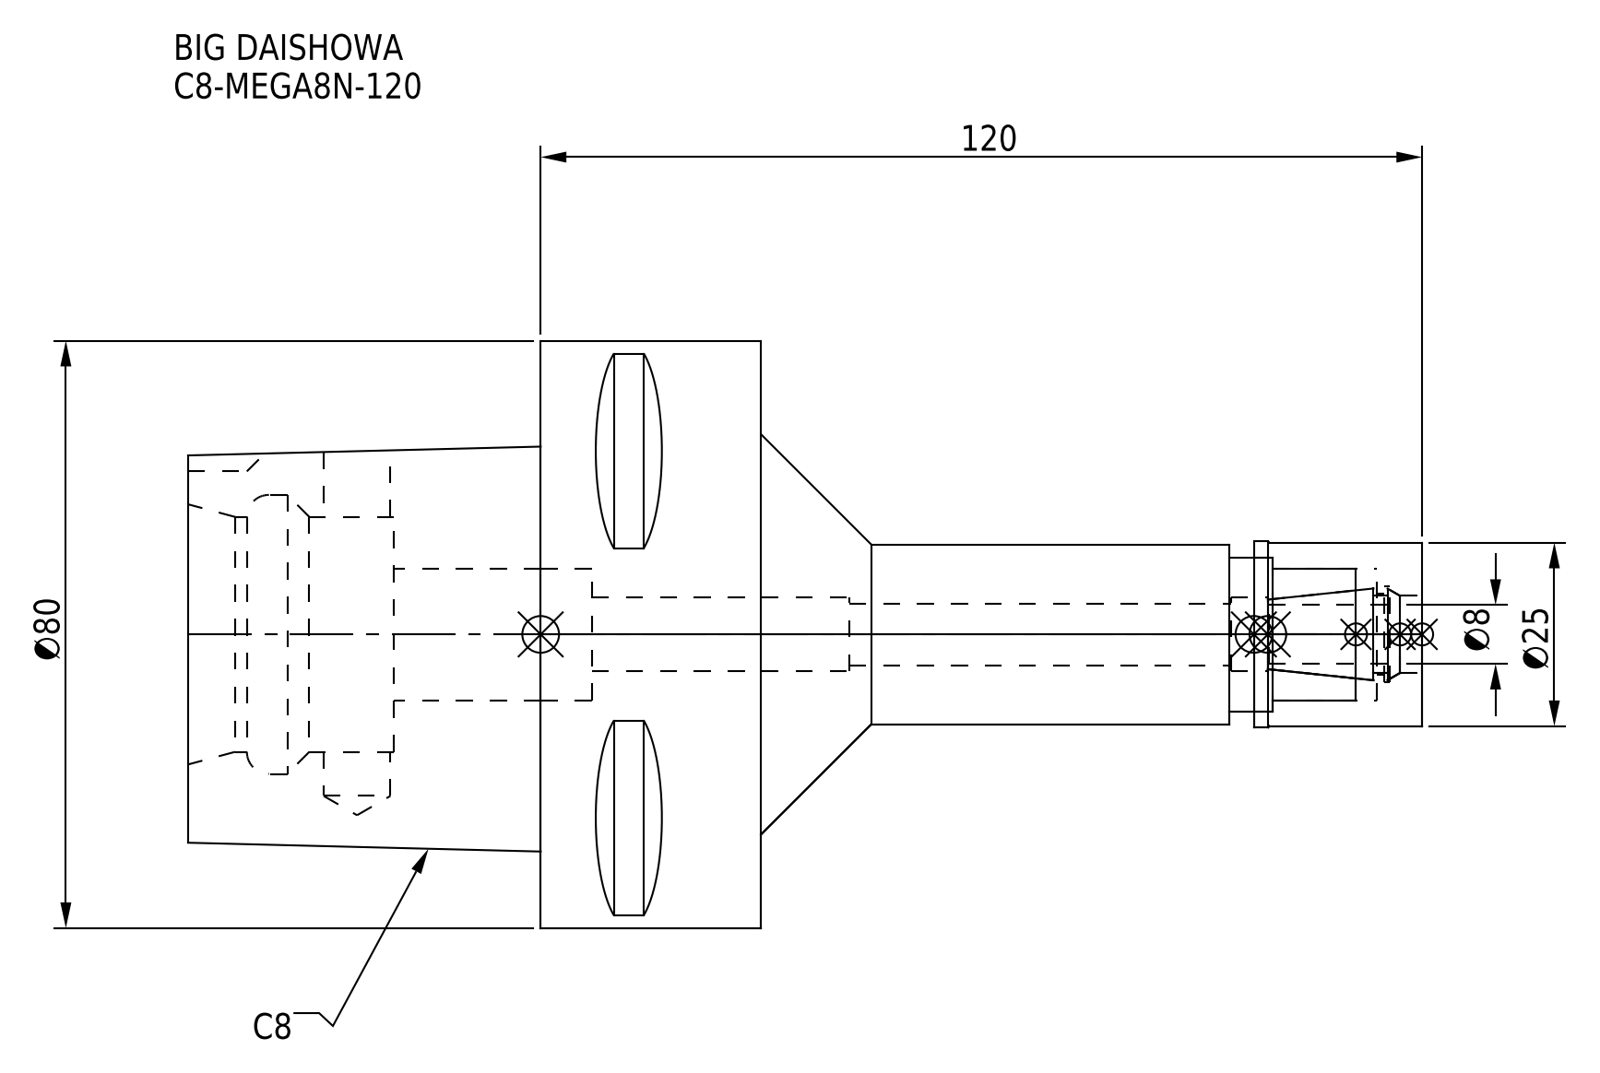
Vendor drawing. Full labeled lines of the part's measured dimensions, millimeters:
Part name (STEP PRODUCT): DXF_TEMP_ASSY_ASM_4_ASM.stp; C8-MEGA8N-120-080.stp; C8-MEGA8N-120; MGN8_1.stp (+3 more)
STEP written by: SolidWorks 2019 (CONFIG_CONTROL_DESIGN)
Units: millimetres
Bodies: 2 solids, 98 faces (39 planar, 41 cylindrical, 18 other)
Overall size (bounding box): 168 × 80 × 80
Volume: 269 418 mm³ · Surface area: 43 349 mm²
Round holes (diameter × count): ⌀8.4 ×1, ⌀9.1 ×1, ⌀10 ×1, ⌀10.5 ×1, ⌀11 ×1, ⌀13 ×1, ⌀18 ×1, ⌀21 ×1, ⌀32 ×1, ⌀38 ×1
Round bosses / shafts (diameter × count): ⌀80 ×1, ⌀25.3 ×1, ⌀25 ×1, ⌀24.5 ×1
Partial cylindrical surfaces — rounded edges, fillets, slot ends (radius × count): R6 ×1
Main face-to-face distances: 30, 78, 48, 20, 50, 28, 90, 32.55, 120, 140
